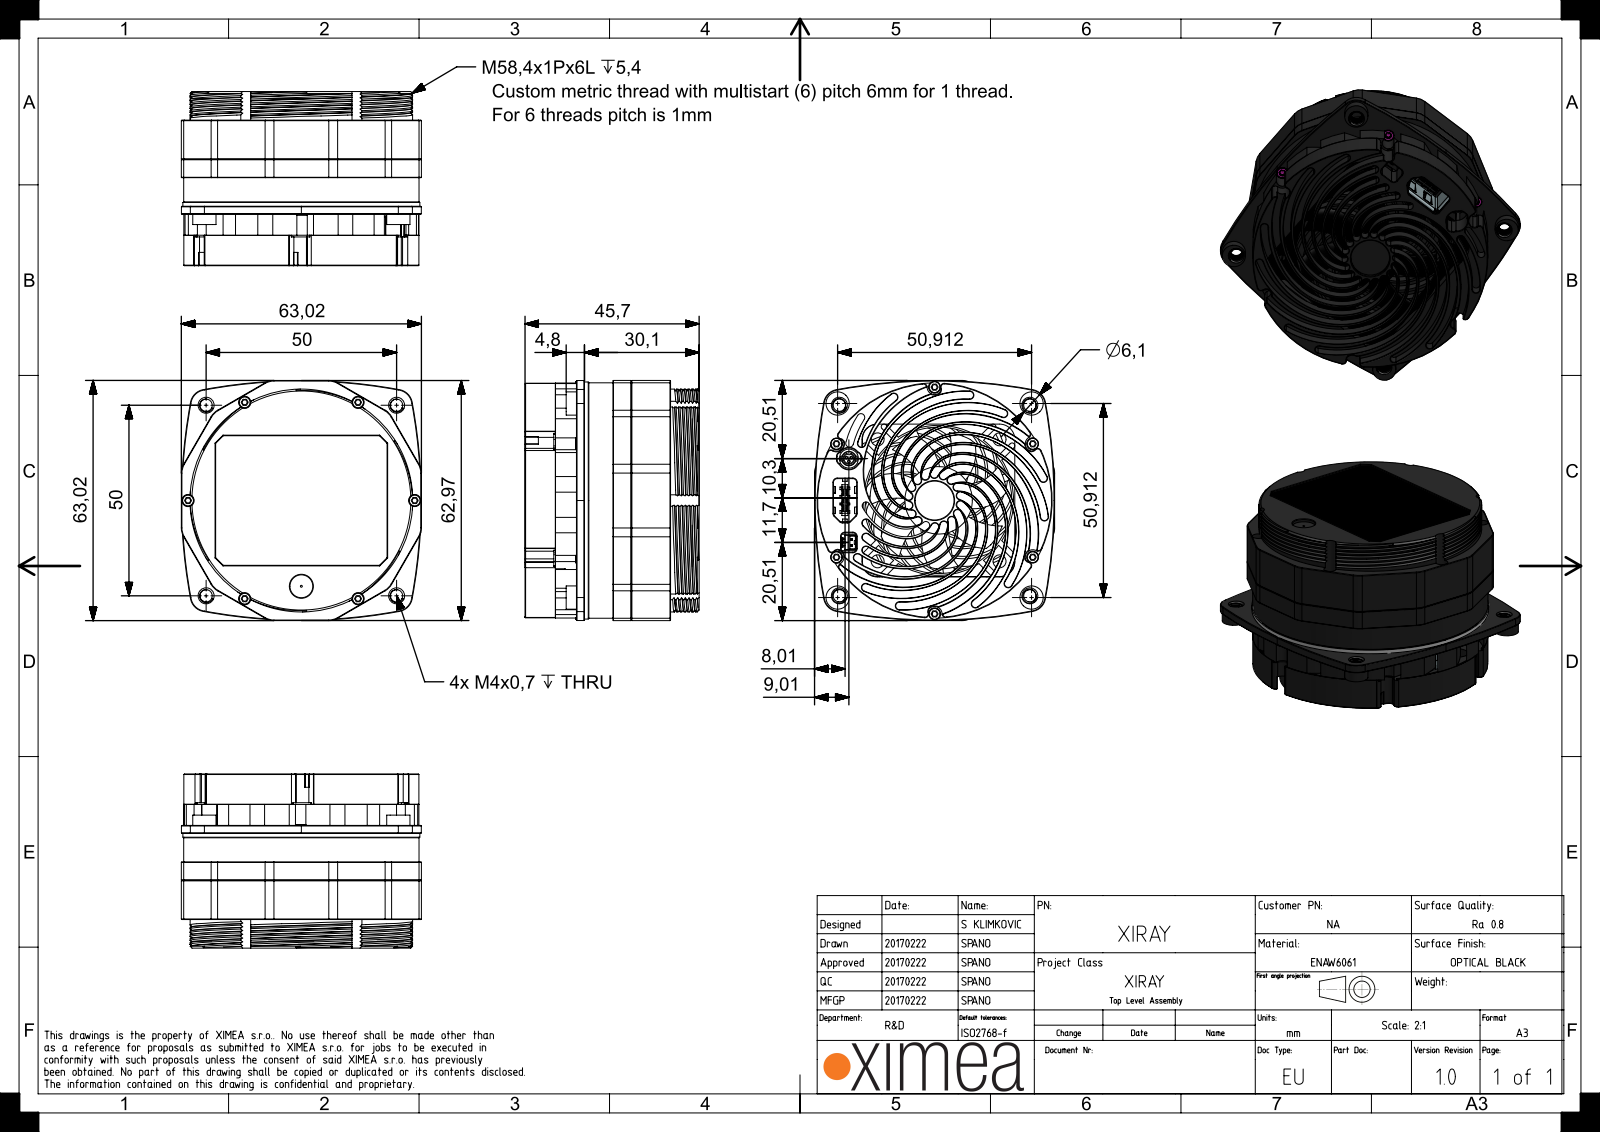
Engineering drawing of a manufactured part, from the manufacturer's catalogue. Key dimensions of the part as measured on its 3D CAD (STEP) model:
Part name (STEP PRODUCT): fan-core; fan-frame; SCREW_A96501606TX-4; SCREW_A96501606TX-8 (+8 more)
STEP written by: SIEMENS PLM Software NX 11.0 (AP203_CONFIGURATION_CONTROLLED_3D_DESIGN_OF_MECHANICAL_PARTS_AND_ASSEMBLIES_MIM_LF)
Units: millimetres
Bodies: 81 solids, 3182 faces (1207 planar, 1176 cylindrical, 799 other)
Overall size (bounding box): 63.02 × 63.02 × 45.7
Volume: 56 244 mm³ · Surface area: 83 398 mm²
Round holes (diameter × count): ⌀1.3 ×18, ⌀1.6 ×12, ⌀3.2 ×10, ⌀1.36 ×6, ⌀3.4 ×4, ⌀4 ×4, ⌀0.51 ×3, ⌀2.4 ×2, ⌀0.5 ×1, ⌀3.8 ×1, ⌀6 ×1, ⌀6.4 ×1
Round bosses / shafts (diameter × count): ⌀0.46 ×40, ⌀2.95 ×12, ⌀6.1 ×4, ⌀61.77 ×1, ⌀61.7 ×1, ⌀60.6 ×1, ⌀58.47 ×1, ⌀39.35 ×1
Partial cylindrical surfaces — rounded edges, fillets, slot ends (radius × count): R1 ×173, R0.2 ×155, R0.3 ×85, R0.5 ×60, R0.4 ×37, R3 ×37, R0.99 ×24, R0.8 ×18
Main face-to-face distances: 1, 4.5, 3.5, 4.3, 8.8, 5.5, 2.2, 22.4, 26.9, 27.4
Hole centre spacings: 41.13, 28.4, 56.17, 15.11, 29.1, 29.75, 50.36, 51.52
